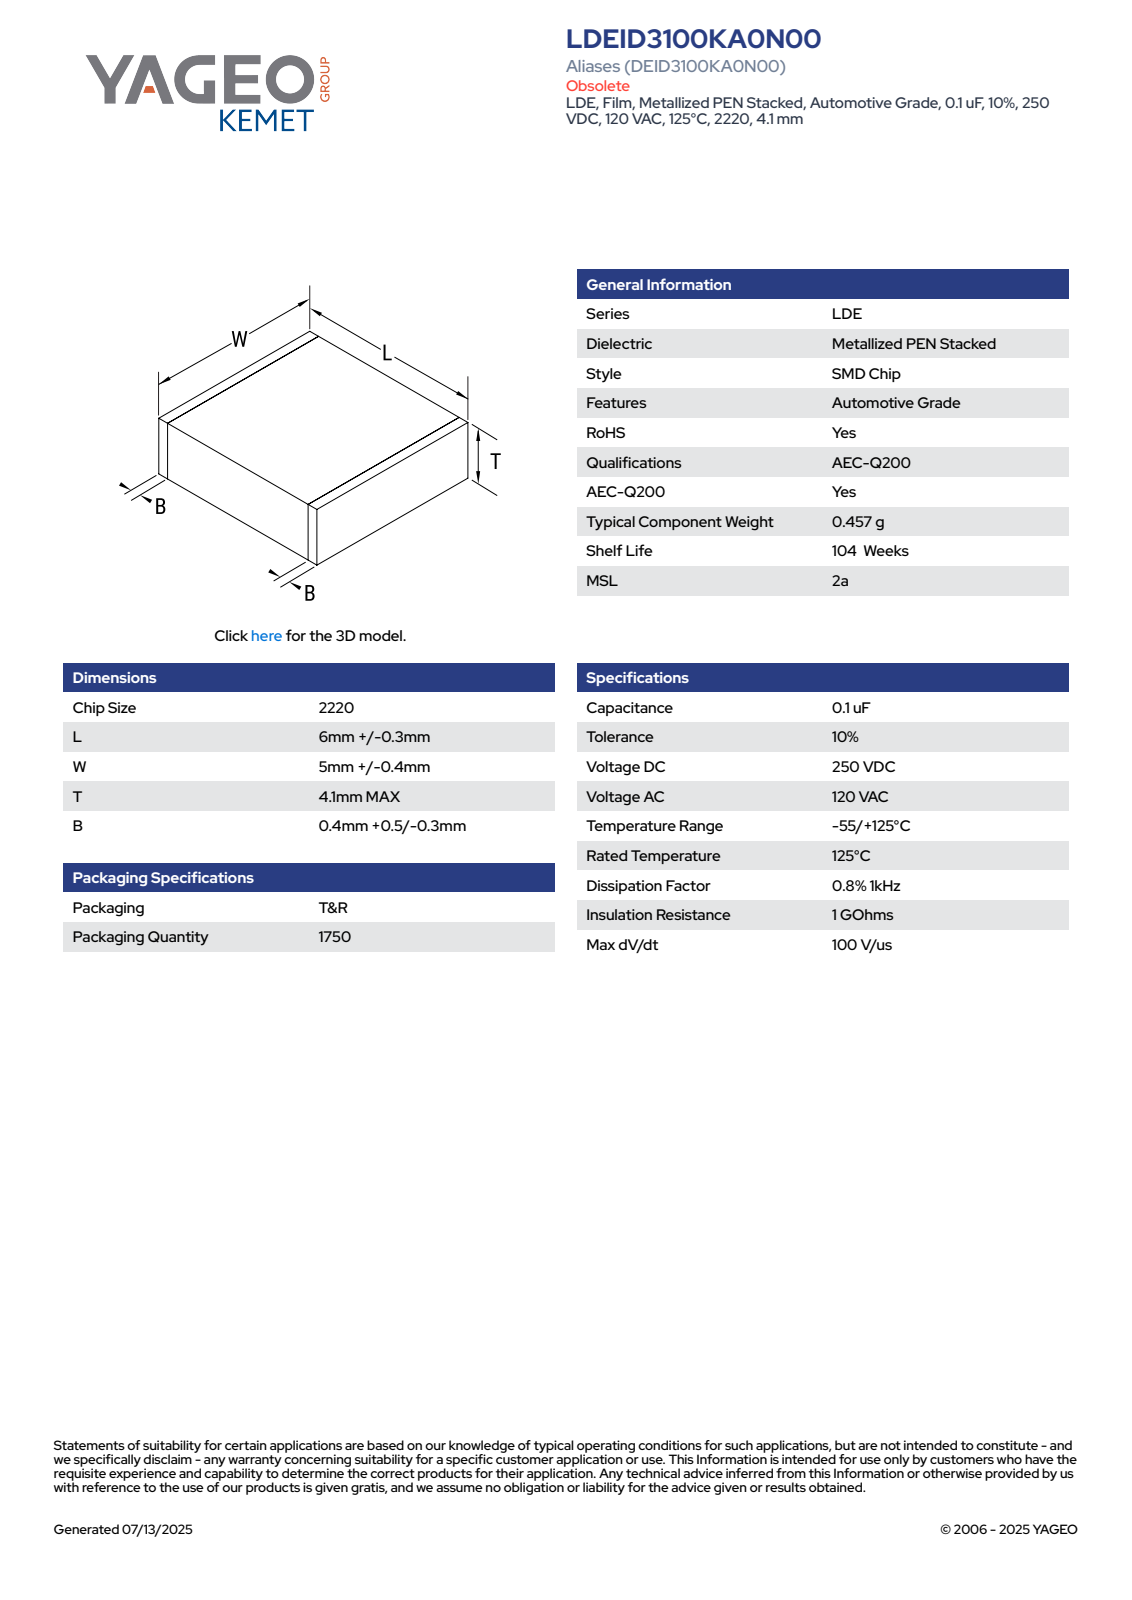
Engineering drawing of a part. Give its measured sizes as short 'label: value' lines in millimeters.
name: CFS_LDELDB_2220_L6.3W5.4T4.1B0.9
written by: SolidWorks 2020 (AUTOMOTIVE_DESIGN)
unit: mm
bodies: 4 solids, 73 faces (73 planar, 0 cylindrical, 0 other)
size: 6.3 × 5.4 × 4.1
volume: 138 mm³; area: 166 mm²
face distances: 4.08, 6.3, 5.38, 4.09, 5.39, 4.1, 5.4, 0.5, 5.8, 5.3
